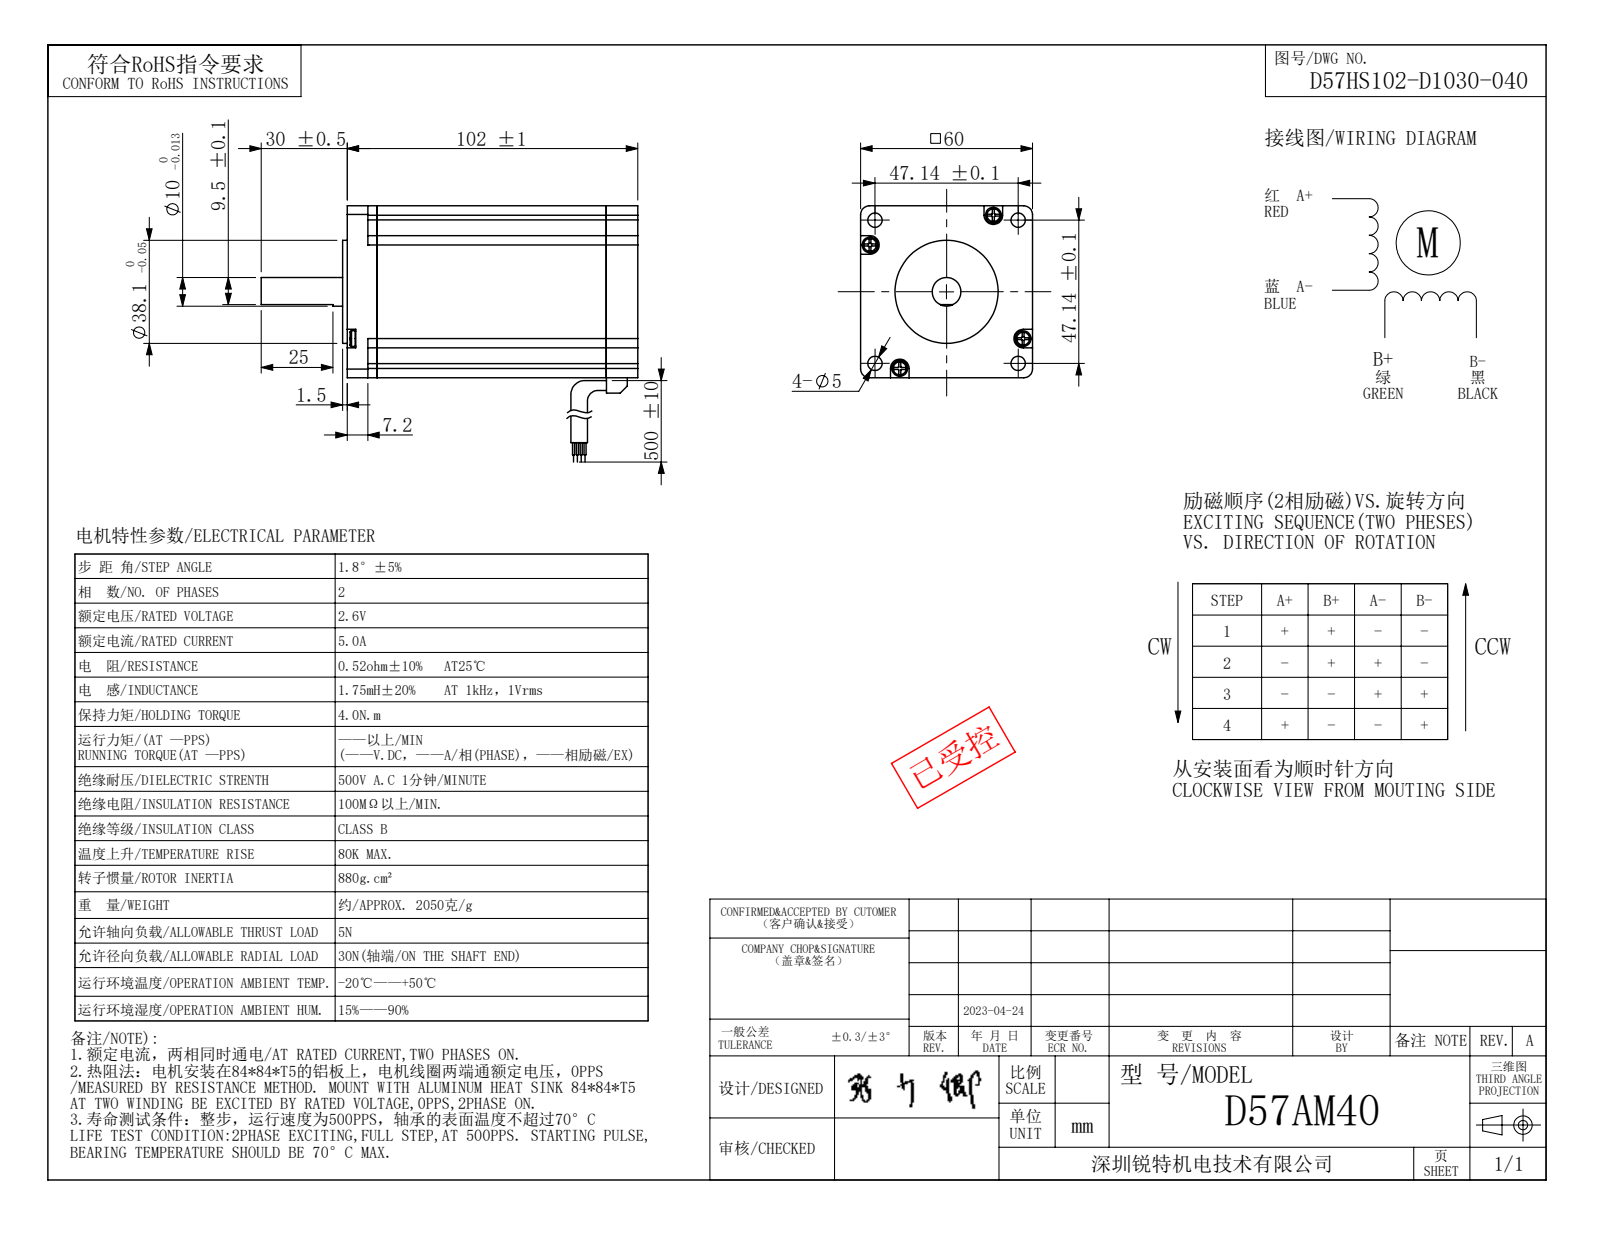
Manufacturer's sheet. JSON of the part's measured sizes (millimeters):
{"part_name": "D57AM40", "step_written_by": "SolidWorks 2020 (CONFIG_CONTROL_DESIGN)", "units": "millimeters", "bodies": {"solids": 3, "faces": 251, "planar": 130, "cylindrical": 121, "other": 0}, "overall_size": [131.5, 60, 60], "volume_mm3": 143650, "surface_area_mm2": 64005, "round_holes": [[2.5, 4], [3.5, 4], [5, 4], [13, 1], [15.4, 1], [17.8, 1], [18, 1], [22, 1], [56, 1]], "round_bosses_or_shafts": [[40, 1], [39, 1], [38.1, 1], [10, 1]], "partial_cylinders_radius": [[3.25, 8], [3, 4], [3.3, 4], [5.5, 4]], "face_to_face_distances": [60, 91, 75.5, 15.5, 8.4, 10.5, 101.5, 26, 2.6, 88.4], "hole_center_spacings": [7.89, 31.35, 33.33, 40.05, 44.34, 47.14, 50.84, 64.23]}
